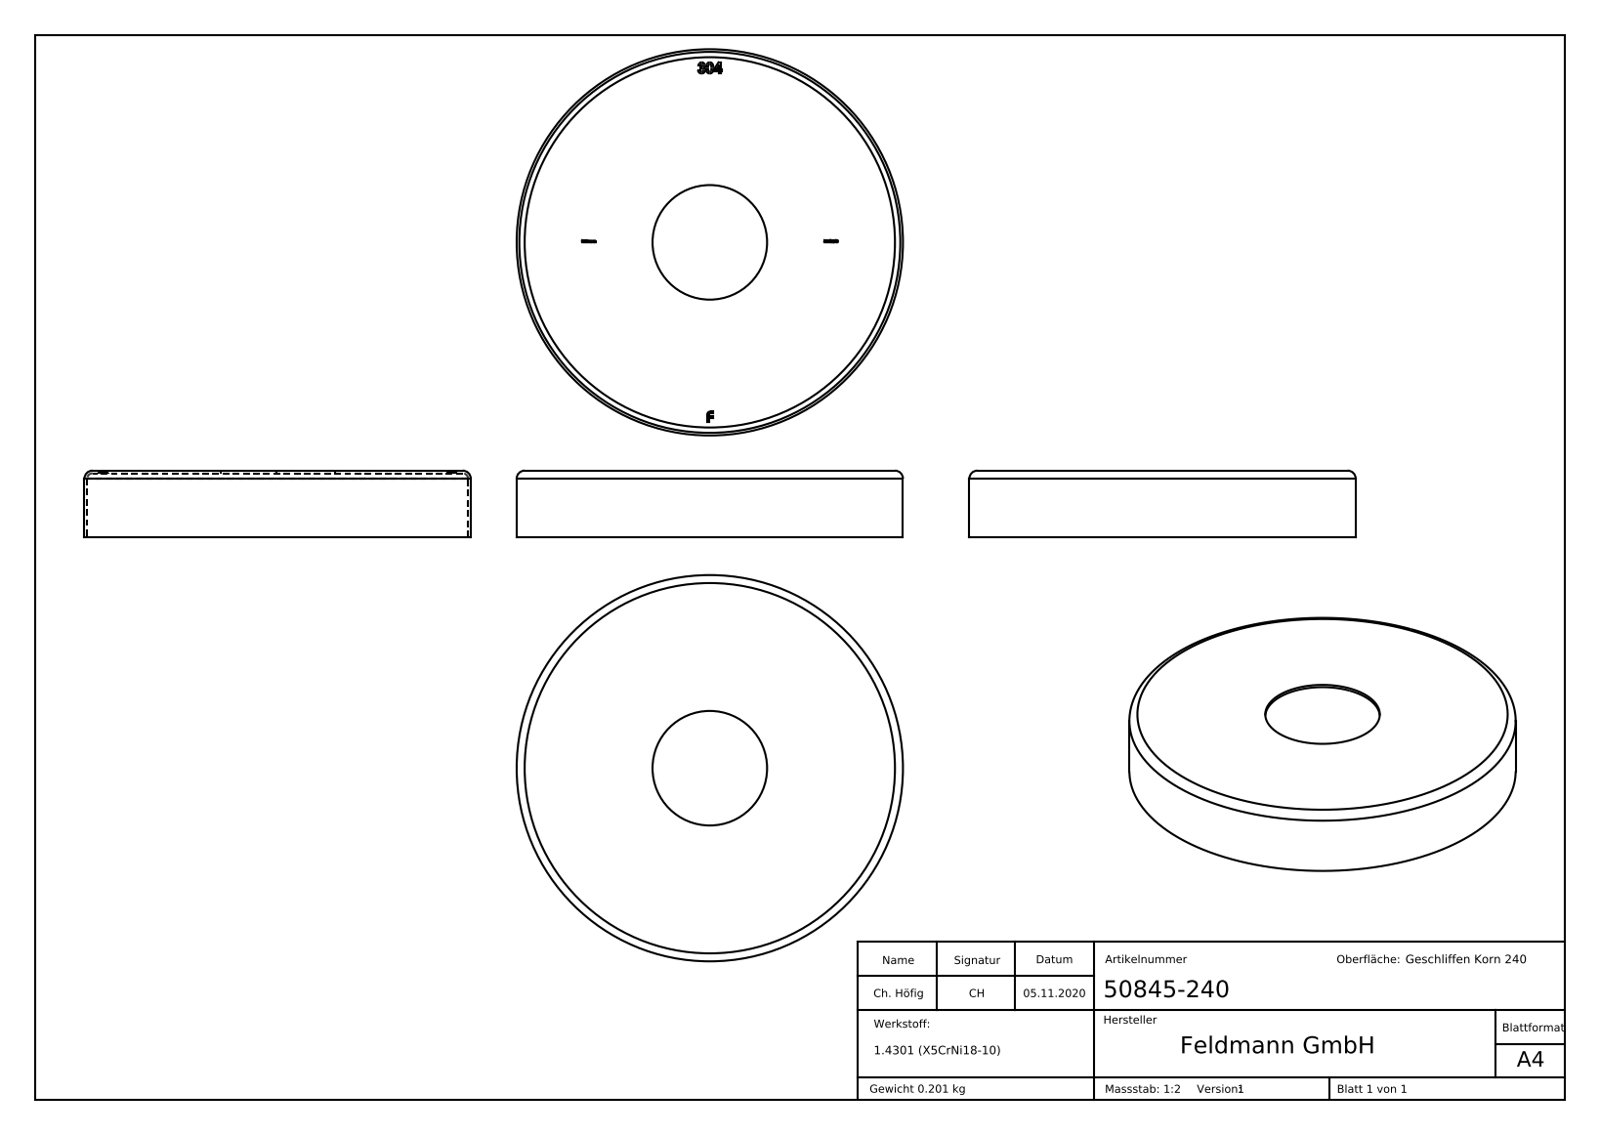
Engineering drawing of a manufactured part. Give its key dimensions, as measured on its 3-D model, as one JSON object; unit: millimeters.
{"part_name": "50845-240", "step_written_by": "SolidWorks 2018 (CONFIG_CONTROL_DESIGN)", "units": "millimeters", "bodies": {"solids": 1, "faces": 304, "planar": 164, "cylindrical": 6, "other": 134}, "overall_size": [145, 145, 25], "volume_mm3": 25427, "surface_area_mm2": 51461, "round_holes": [[43, 1], [143, 1]], "round_bosses_or_shafts": [[145, 1]], "face_to_face_distances": [1, 24, 25, 24.1, 0.9, 0.71, 5, 4.29, 0.58, 0.69]}
